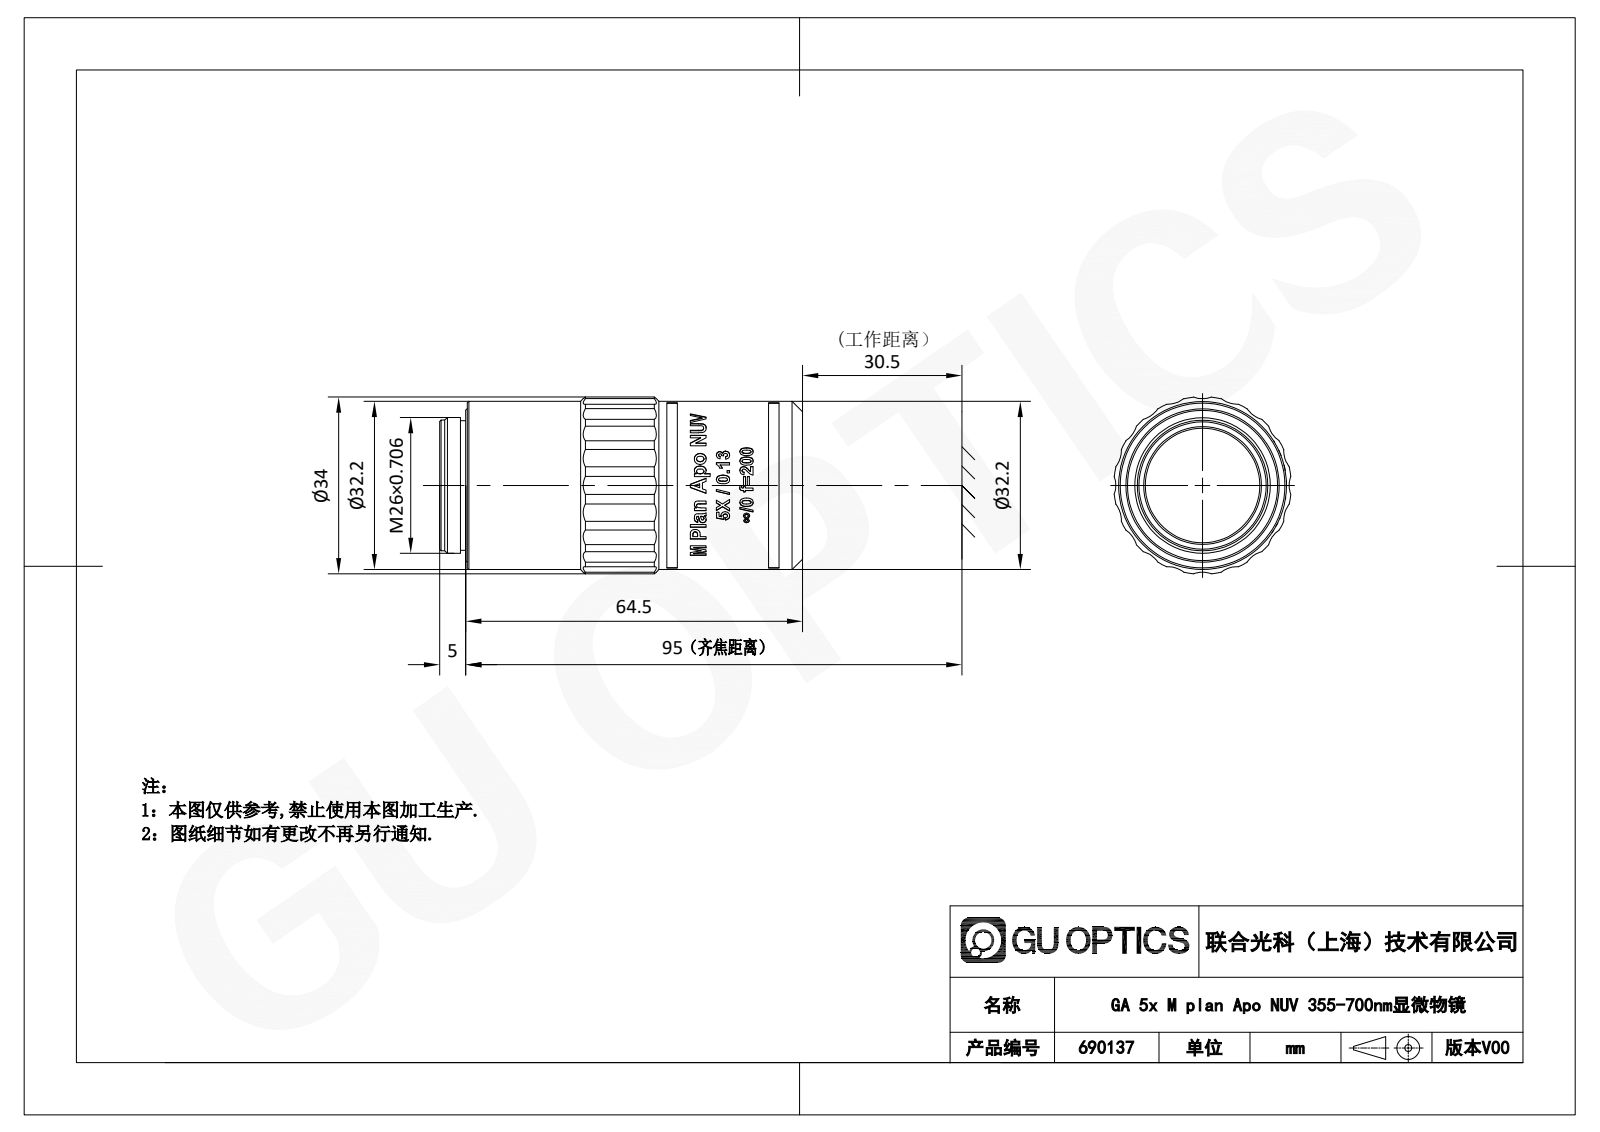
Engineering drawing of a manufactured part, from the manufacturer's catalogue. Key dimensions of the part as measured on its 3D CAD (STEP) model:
Part name (STEP PRODUCT): 690137
STEP written by: SolidWorks 2020 (CONFIG_CONTROL_DESIGN)
Units: millimetres
Bodies: 1 solid, 436 faces (122 planar, 98 cylindrical, 216 other)
Overall size (bounding box): 69.5 × 33.82 × 33.82
Volume: 54 023 mm³ · Surface area: 9 007 mm²
Round holes (diameter × count): ⌀20 ×1, ⌀22 ×1
Round bosses / shafts (diameter × count): ⌀32.2 ×1, ⌀32 ×1, ⌀26 ×1, ⌀25 ×1, ⌀24.8 ×1
Partial cylindrical surfaces — rounded edges, fillets, slot ends (radius × count): R5 ×20, R17 ×1
Main face-to-face distances: 65.8, 1.3, 64.5, 1.6, 64.2, 5, 3.7, 5.3, 69.5, 4
